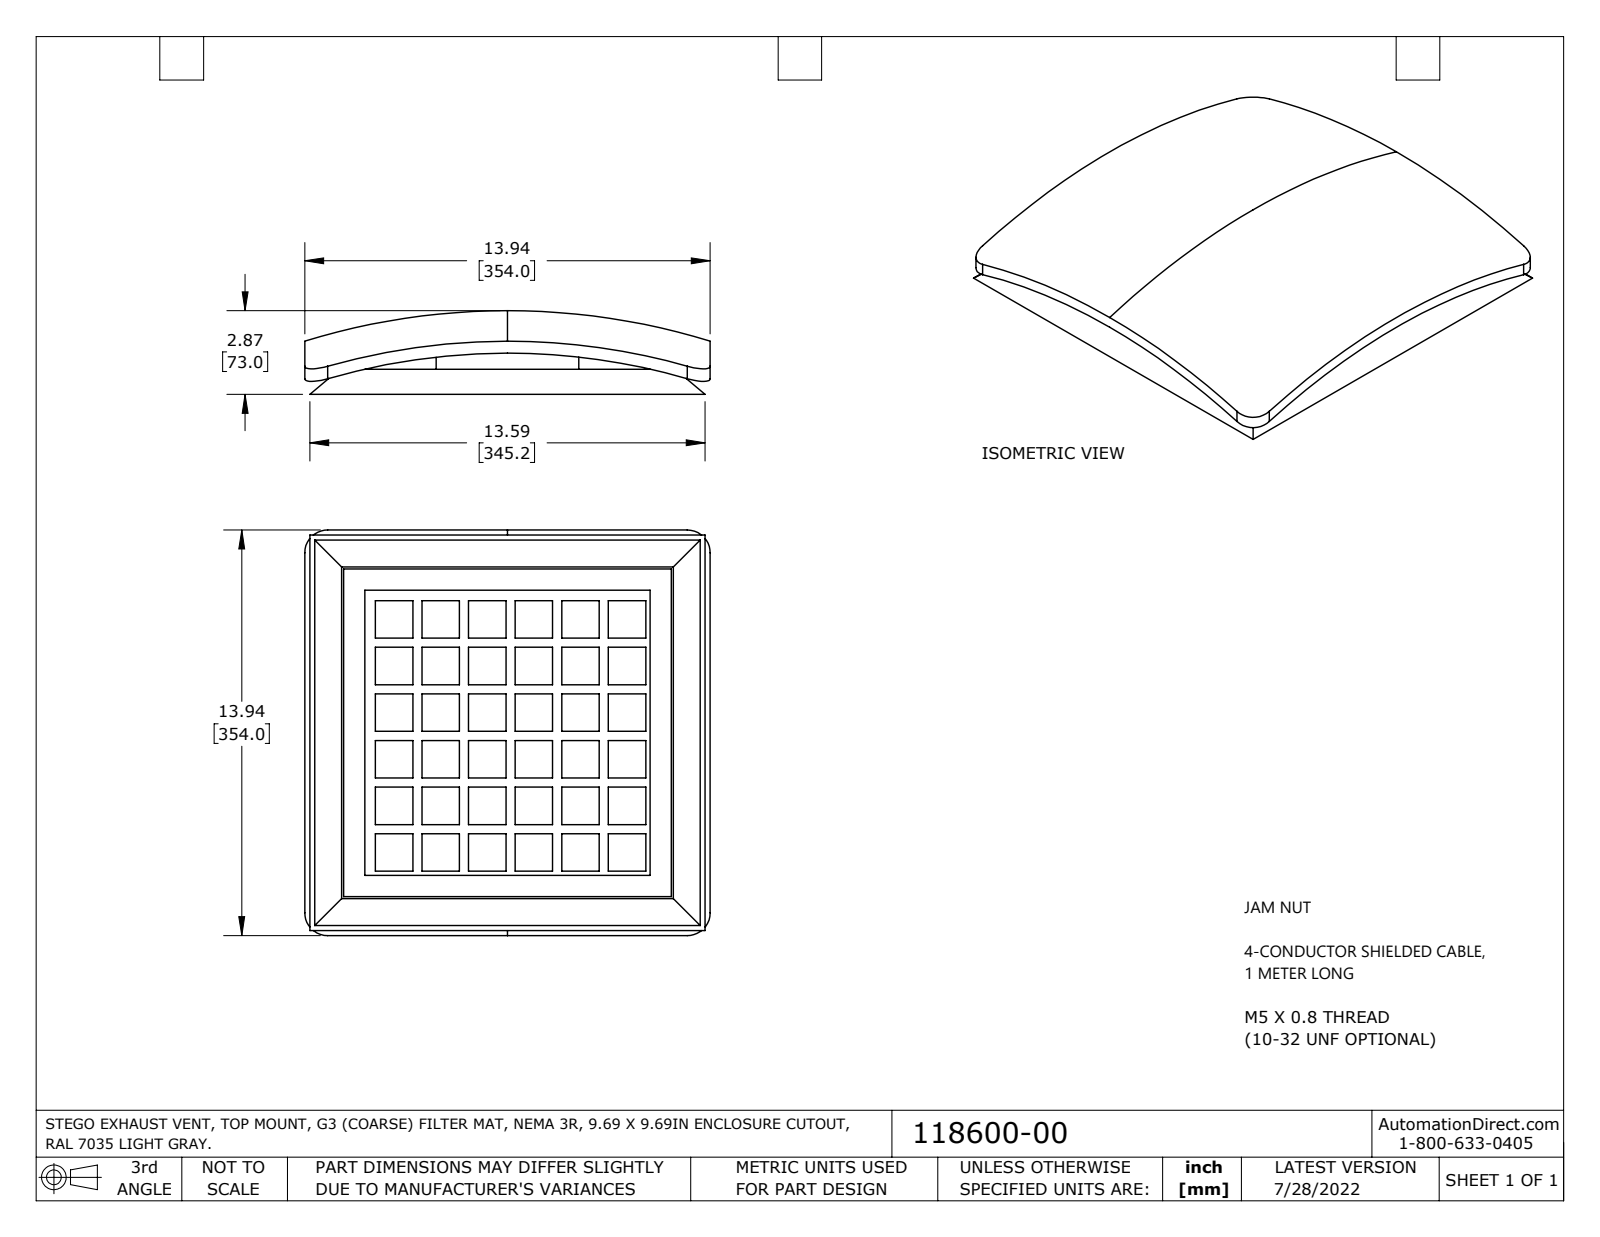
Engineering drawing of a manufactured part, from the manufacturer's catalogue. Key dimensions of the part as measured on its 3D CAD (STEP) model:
Part name (STEP PRODUCT): 118600-00_Default
STEP written by: SolidWorks 2021 (CONFIG_CONTROL_DESIGN)
Units: inches
Bodies: 1 solid, 229 faces (221 planar, 4 cylindrical, 4 other)
Overall size (bounding box): 13.937 × 13.937 × 2.874
Volume: 166.5 in³ · Surface area: 946.5 in²
Partial cylindrical surfaces — rounded edges, fillets, slot ends (radius × count): R0.787 ×4
Main face-to-face distances: 0.431, 0.109, 0.862, 0.172, 0.259, 0.69, 1.601, 0.728, 10.531, 1.339
